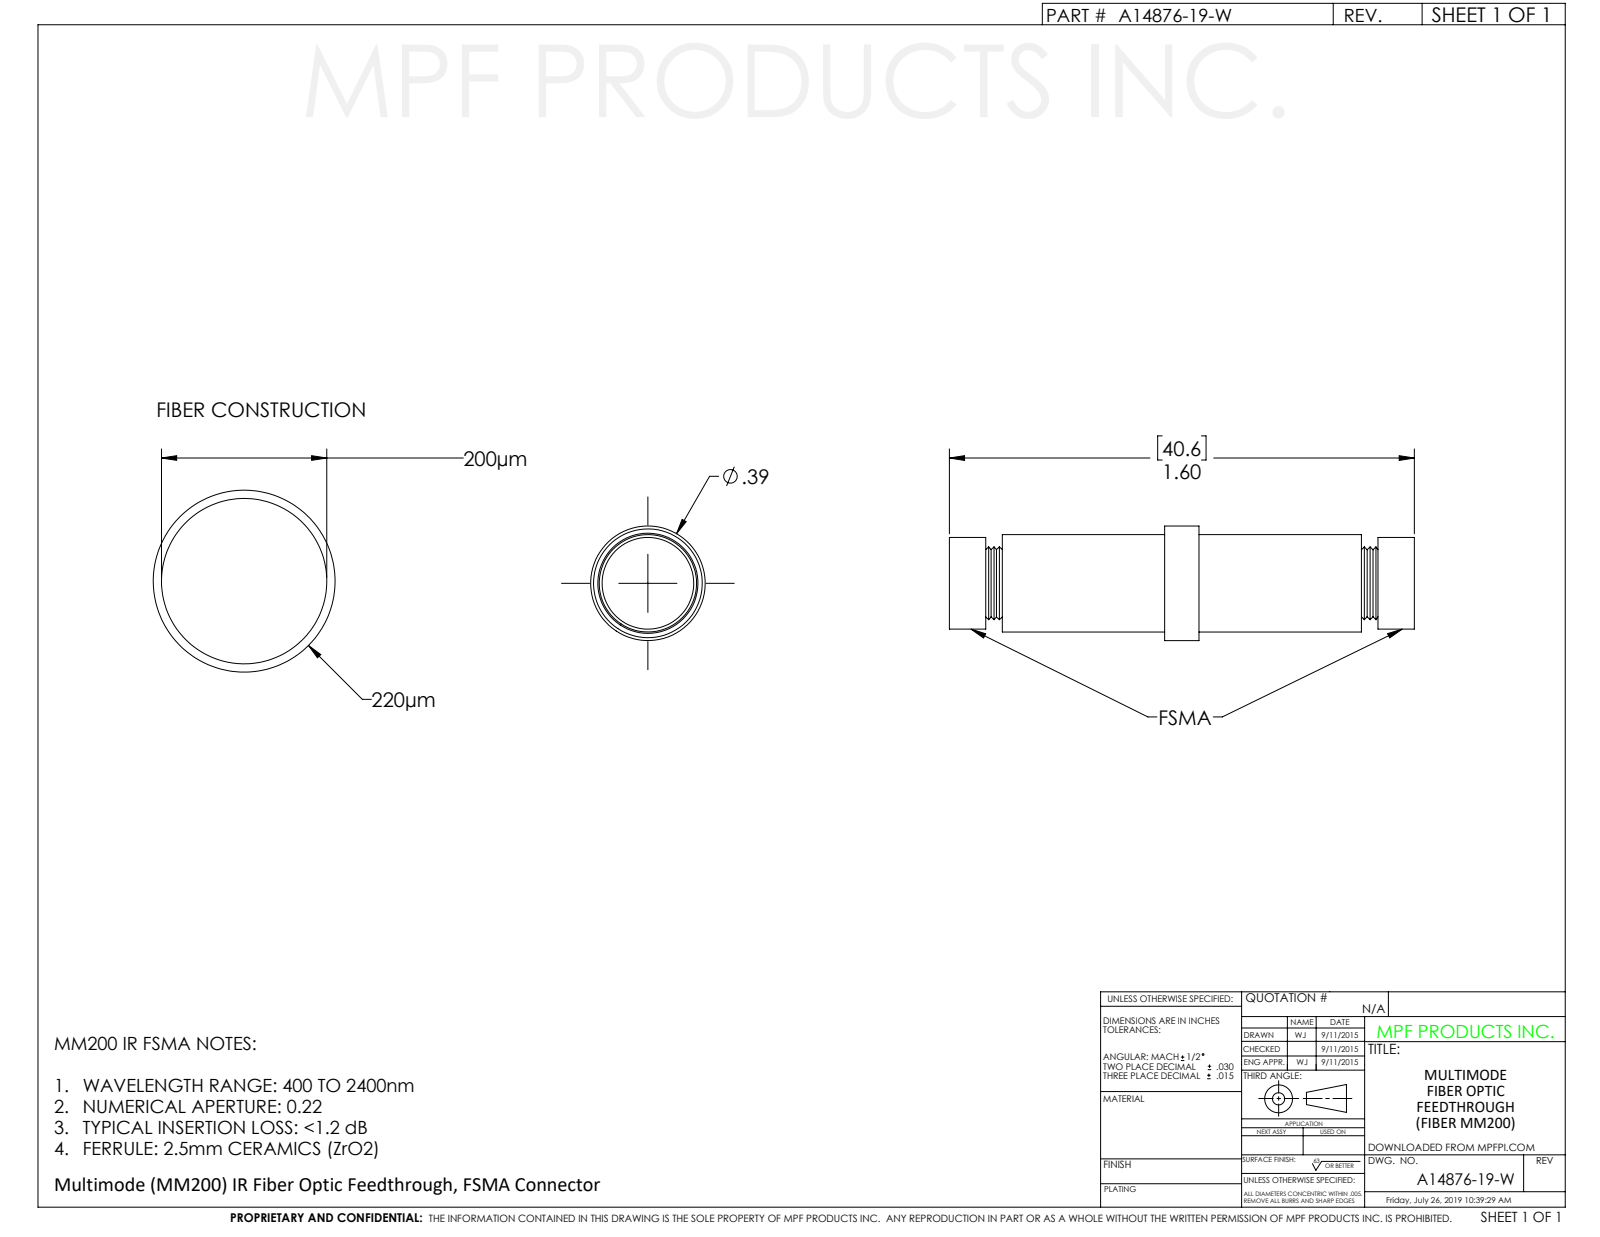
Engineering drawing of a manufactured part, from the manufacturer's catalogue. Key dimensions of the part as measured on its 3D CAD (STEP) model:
Part name (STEP PRODUCT): A14876-19-W
STEP written by: SolidWorks 2019 (CONFIG_CONTROL_DESIGN)
Units: inches
Bodies: 1 solid, 48 faces (10 planar, 14 cylindrical, 24 other)
Overall size (bounding box): 1.598 × 0.394 × 0.394
Volume: 0.137 in³ · Surface area: 2.1 in²
Round holes (diameter × count): ⌀0.374 ×1
Round bosses / shafts (diameter × count): ⌀0.394 ×1, ⌀0.344 ×1, ⌀0.335 ×1, ⌀0.315 ×1
Main face-to-face distances: 0.182, 1.417, 1.598, 0.74, 0.858, 0.558, 0.676, 1.235, 1.473, 1.291
